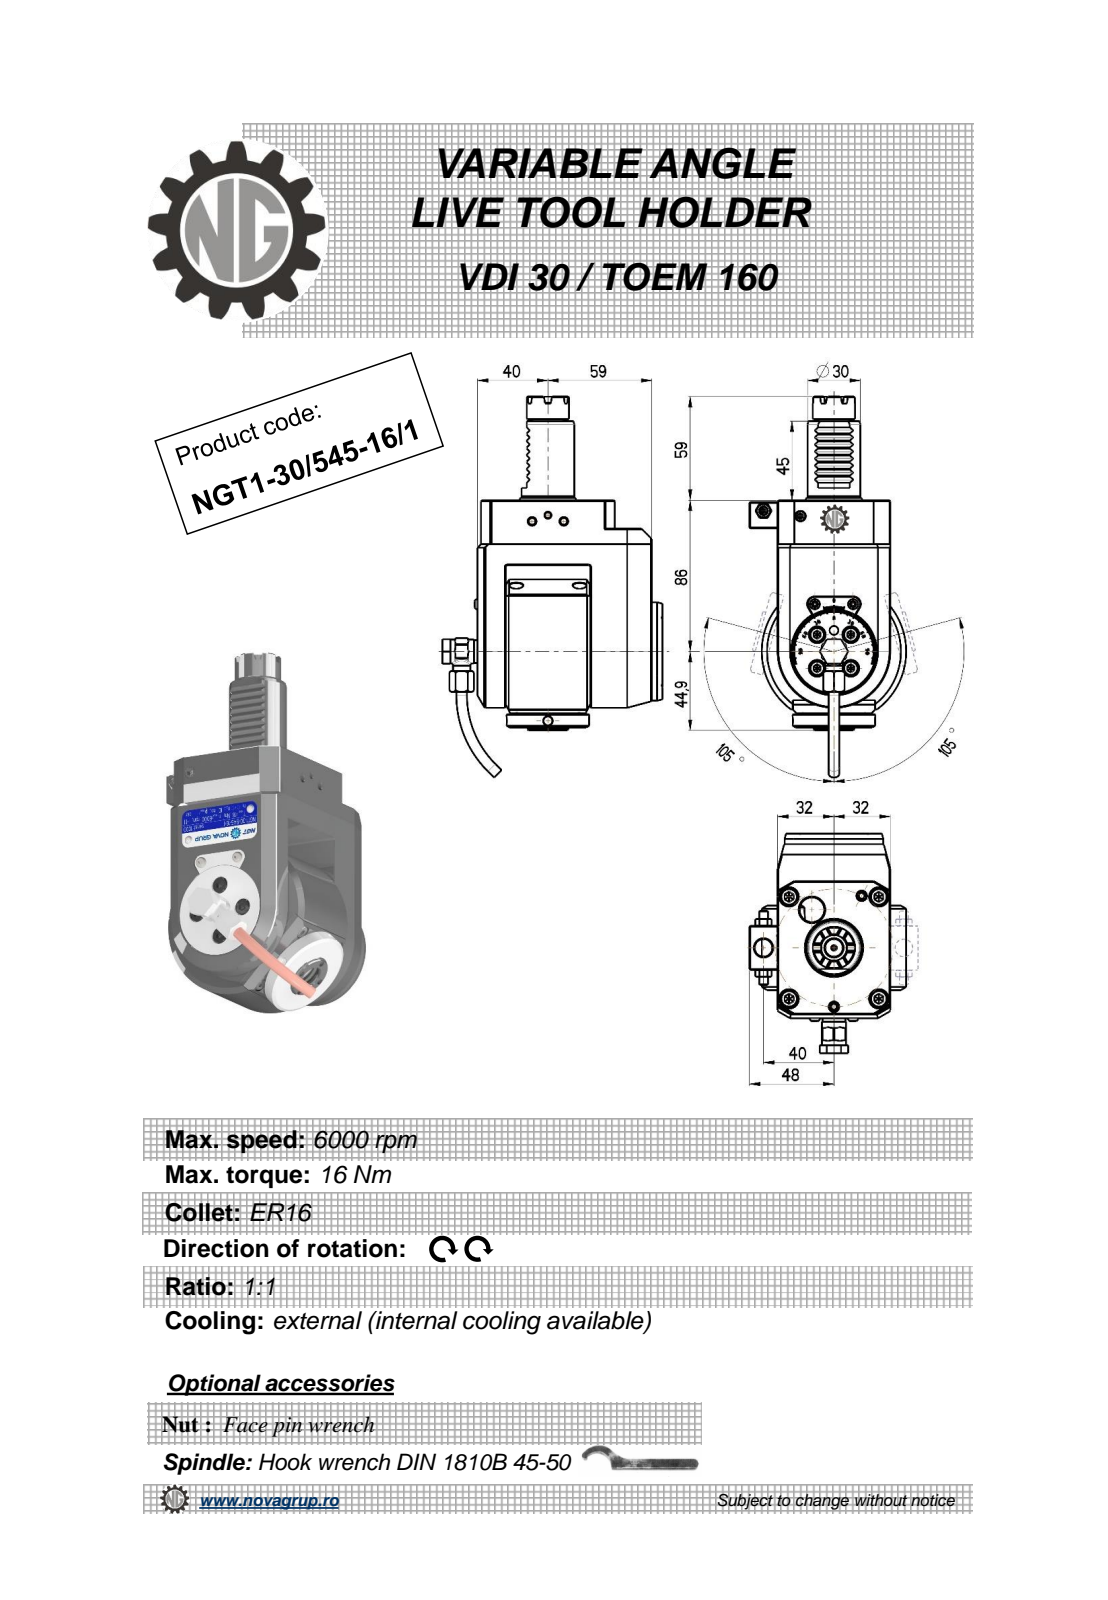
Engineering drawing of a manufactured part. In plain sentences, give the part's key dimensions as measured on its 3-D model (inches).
The part is named "NGT1_30_545_16_1". Its 3-D file was written by "PRO/ENGINEER BY PARAMETRIC TECHNOLOGY CORPORATION, 2010280 (CONFIG_CONTROL_DESIGN)". It is 1 solid with 524 faces: 229 planar, 138 cylindrical and 157 other. Overall it measures 8.53 by 4.917 by 3.504 inches. Its volume is 46.23 cubic inches and its surface area 111 square inches. Round holes: 4 of diameter 0.126, 3 of diameter 0.157, 2 of diameter 0.197, 2 of diameter 0.394, 1 of diameter 0.118, 1 of diameter 0.165, 1 of diameter 0.244, 1 of diameter 0.354, 1 of diameter 0.374, 1 of diameter 0.433, 1 of diameter 0.492. Round bosses or shafts: 2 of diameter 0.236, 2 of diameter 0.224, 1 of diameter 3.228, 1 of diameter 2.205, 1 of diameter 1.85, 1 of diameter 1.378, 1 of diameter 1.181, 1 of diameter 0.945. Partial cylindrical surfaces (rounded edges, fillets, slot ends): 12 of radius 0.01, 8 of radius 0.012, 6 of radius 0.006, 4 of radius 0.02, 2 of radius 0.039, 1 of radius 0.303, 1 of radius 1.26. The main face-to-face distances are 2.52, 0.63, 1.457, 3.898, 0.236, 4.134, 3.268, 0.551, 2.441, 1.89. The hole center spacings are 0.364, 0.515, 0.728, 1.617, 1.963, 1.979, 0.016, 1.211.
